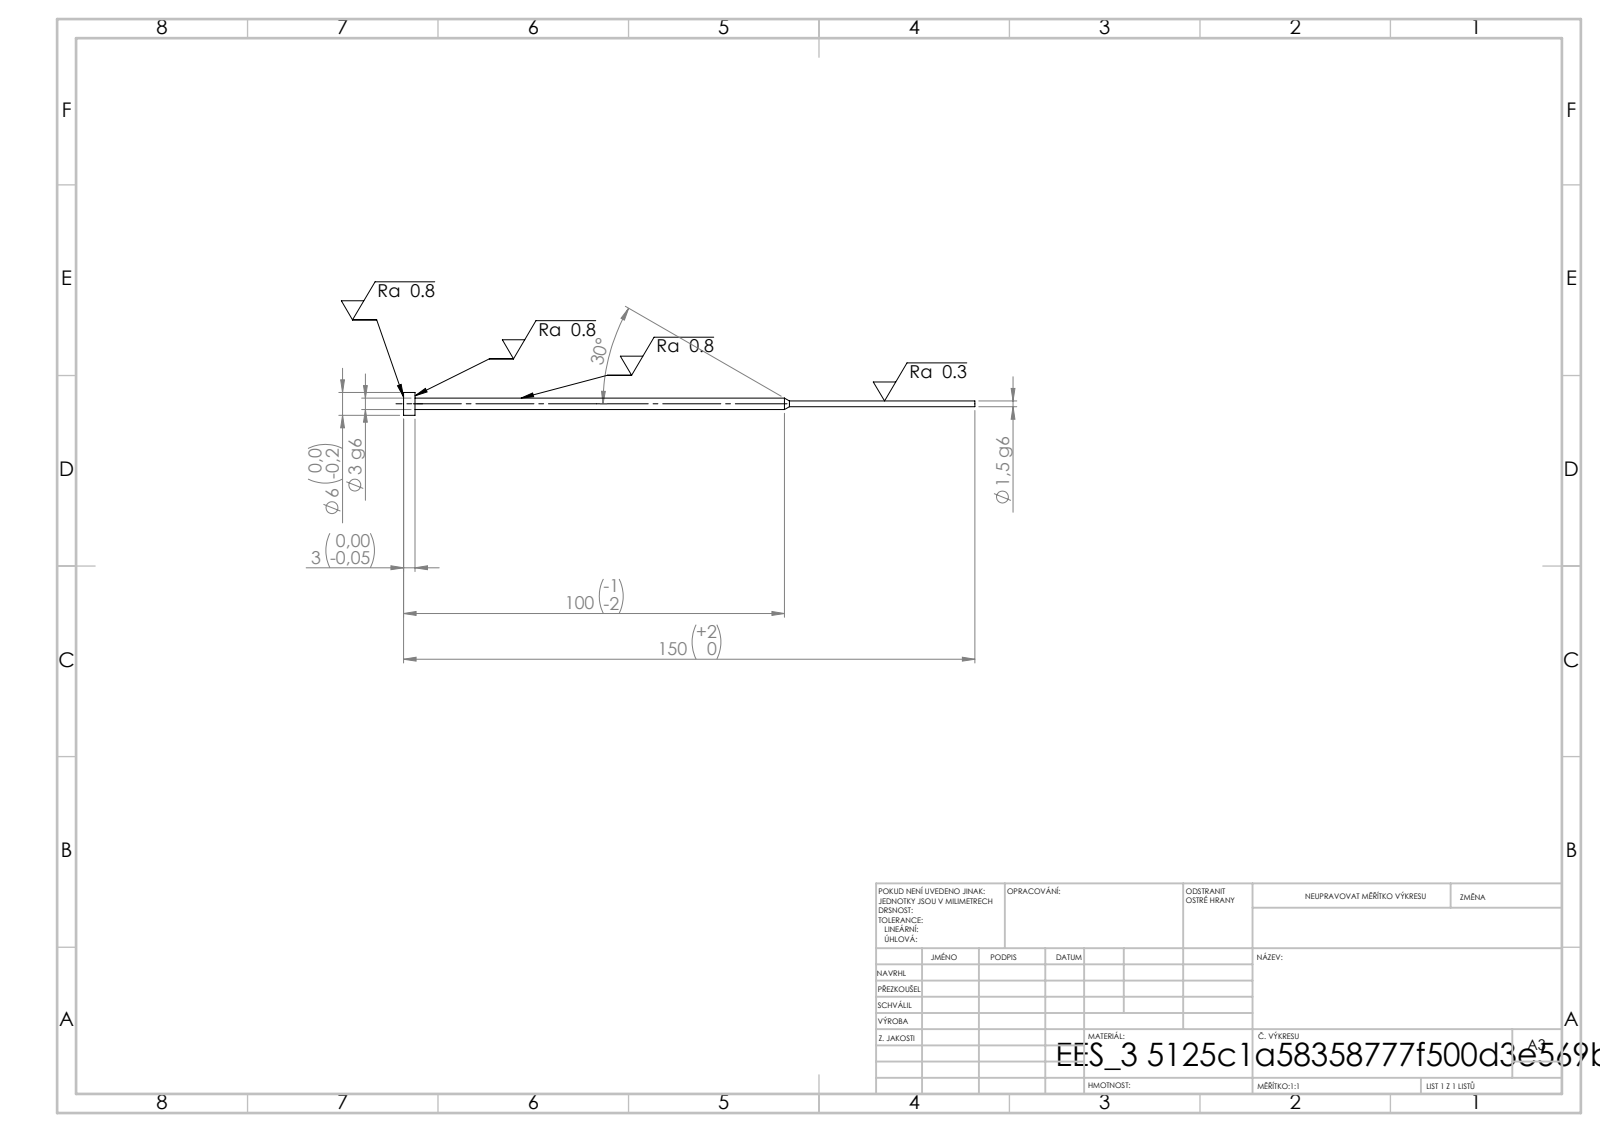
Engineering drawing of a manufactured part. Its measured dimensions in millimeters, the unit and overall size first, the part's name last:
Units: millimetres
Overall size (bounding box): 150 × 6 × 6
Round bosses / shafts (diameter × count): ⌀6 ×1, ⌀3 ×1, ⌀1.5 ×1
Main face-to-face distances: 3, 147, 150
Volume: 862 mm³ · Surface area: 1 262 mm²
Bodies: 1 solid, 11 faces (3 planar, 6 cylindrical, 2 other)
STEP written by: SolidWorks 2019 (CONFIG_CONTROL_DESIGN)
